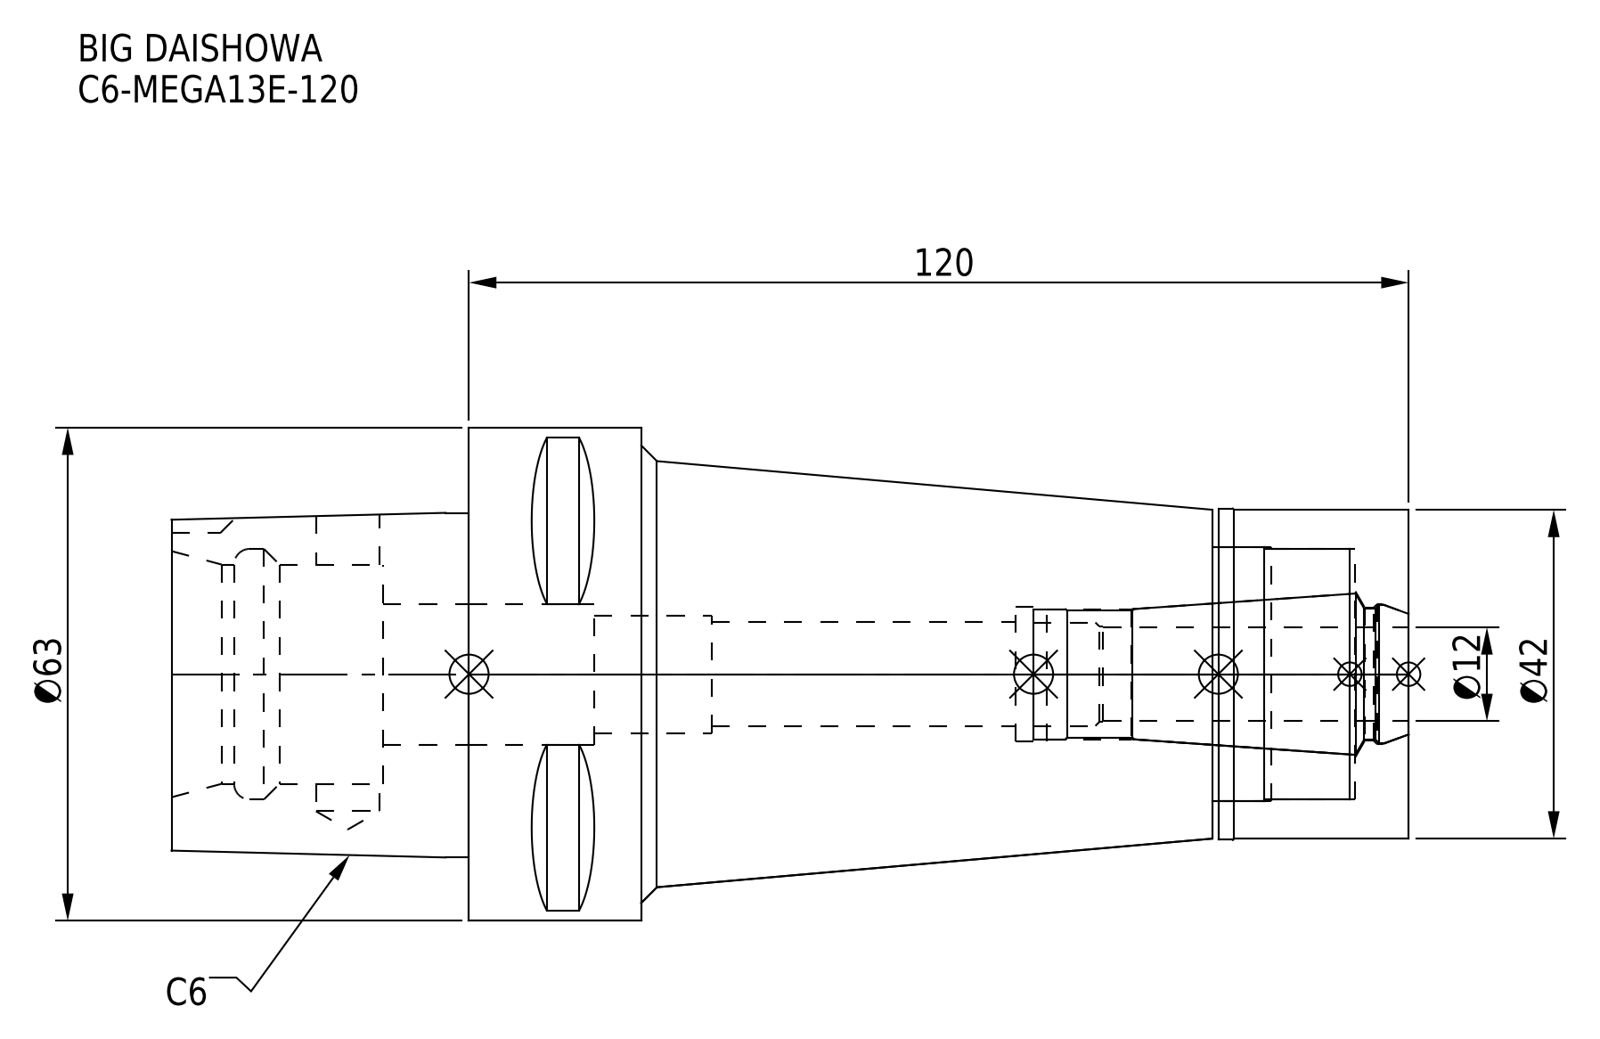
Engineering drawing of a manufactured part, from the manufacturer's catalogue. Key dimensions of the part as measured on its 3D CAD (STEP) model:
Part name (STEP PRODUCT): C6-MEGA13E-120-120_ASM.stp; C6-MEGA13E-120-120.stp; DXF_TEMP_ASSY_ASM_4_ASM.stp; C6-MEGA13E-120-120-FreeParts (+3 more)
STEP written by: SolidWorks 2019 (CONFIG_CONTROL_DESIGN)
Units: millimetres
Bodies: 2 solids, 100 faces (37 planar, 39 cylindrical, 24 other)
Overall size (bounding box): 158 × 63 × 63
Volume: 244 983 mm³ · Surface area: 43 986 mm²
Round holes (diameter × count): ⌀8.1 ×1, ⌀13.3 ×1, ⌀15 ×1, ⌀16.6 ×1, ⌀17 ×1, ⌀17.2 ×1, ⌀17.9 ×1, ⌀18 ×1, ⌀28 ×1, ⌀32 ×1, ⌀32.5 ×1
Round bosses / shafts (diameter × count): ⌀63 ×1, ⌀42.3 ×1, ⌀42 ×1
Partial cylindrical surfaces — rounded edges, fillets, slot ends (radius × count): R5 ×1
Main face-to-face distances: 120, 25.1, 24.3, 95.7, 0.8, 94.9, 112.5, 158, 133.7, 132.9
